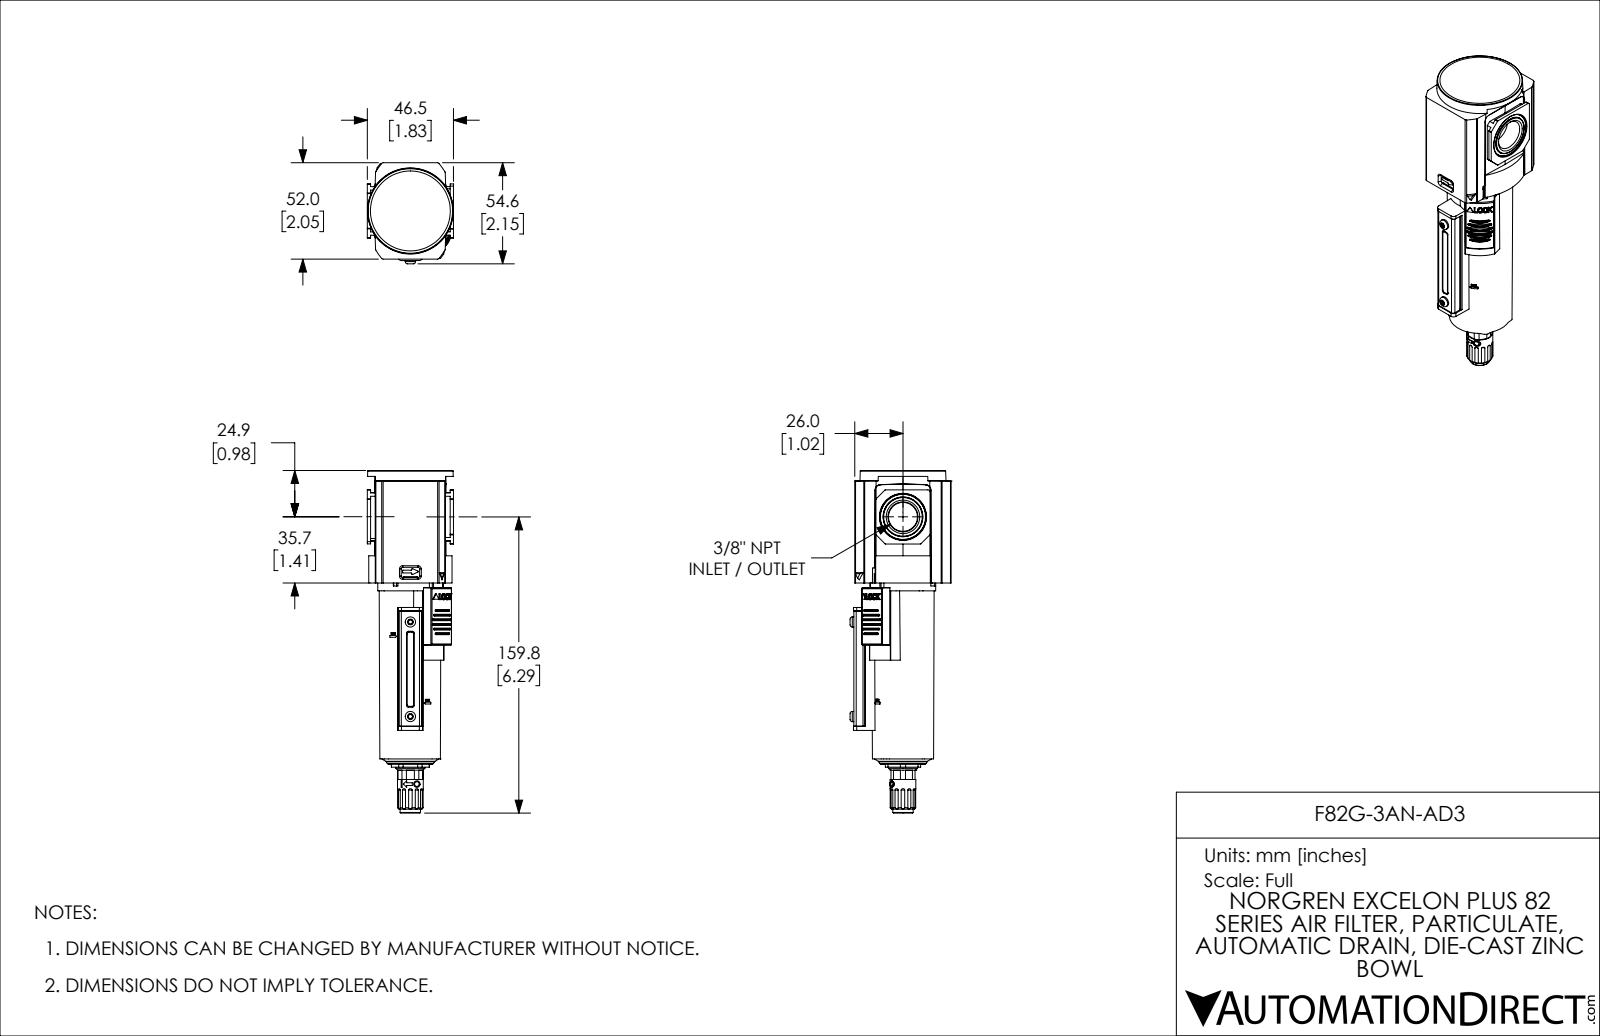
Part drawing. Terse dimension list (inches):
name: F82G-3AN-AD3
written by: SolidWorks 2021 (CONFIG_CONTROL_DESIGN)
unit: in
bodies: 5 solids, 1157 faces (492 planar, 441 cylindrical, 224 other)
size: 7.275 × 2.148 × 1.831
volume: 12.62 in³; area: 89.6 in²
holes: 2× ⌀0.128, 1× ⌀0.098, 1× ⌀0.259, 1× ⌀0.628
bosses: 2× ⌀0.217, 1× ⌀1.388, 1× ⌀1.356, 1× ⌀1.291, 1× ⌀1.257, 1× ⌀0.617, 1× ⌀0.547, 1× ⌀0.539
rounds: 57× R0.039, 54× R0.02, 12× R0.011, 12× R0.019, 10× R0.01, 8× R0.031, 8× R0.036, 8× R0.048
face distances: 0.059, 1.988, 1.467, 2.047, 1.929, 0.058, 2.093, 2.151, 0.182, 1.475
hole spacings: 0.594, 1.189
